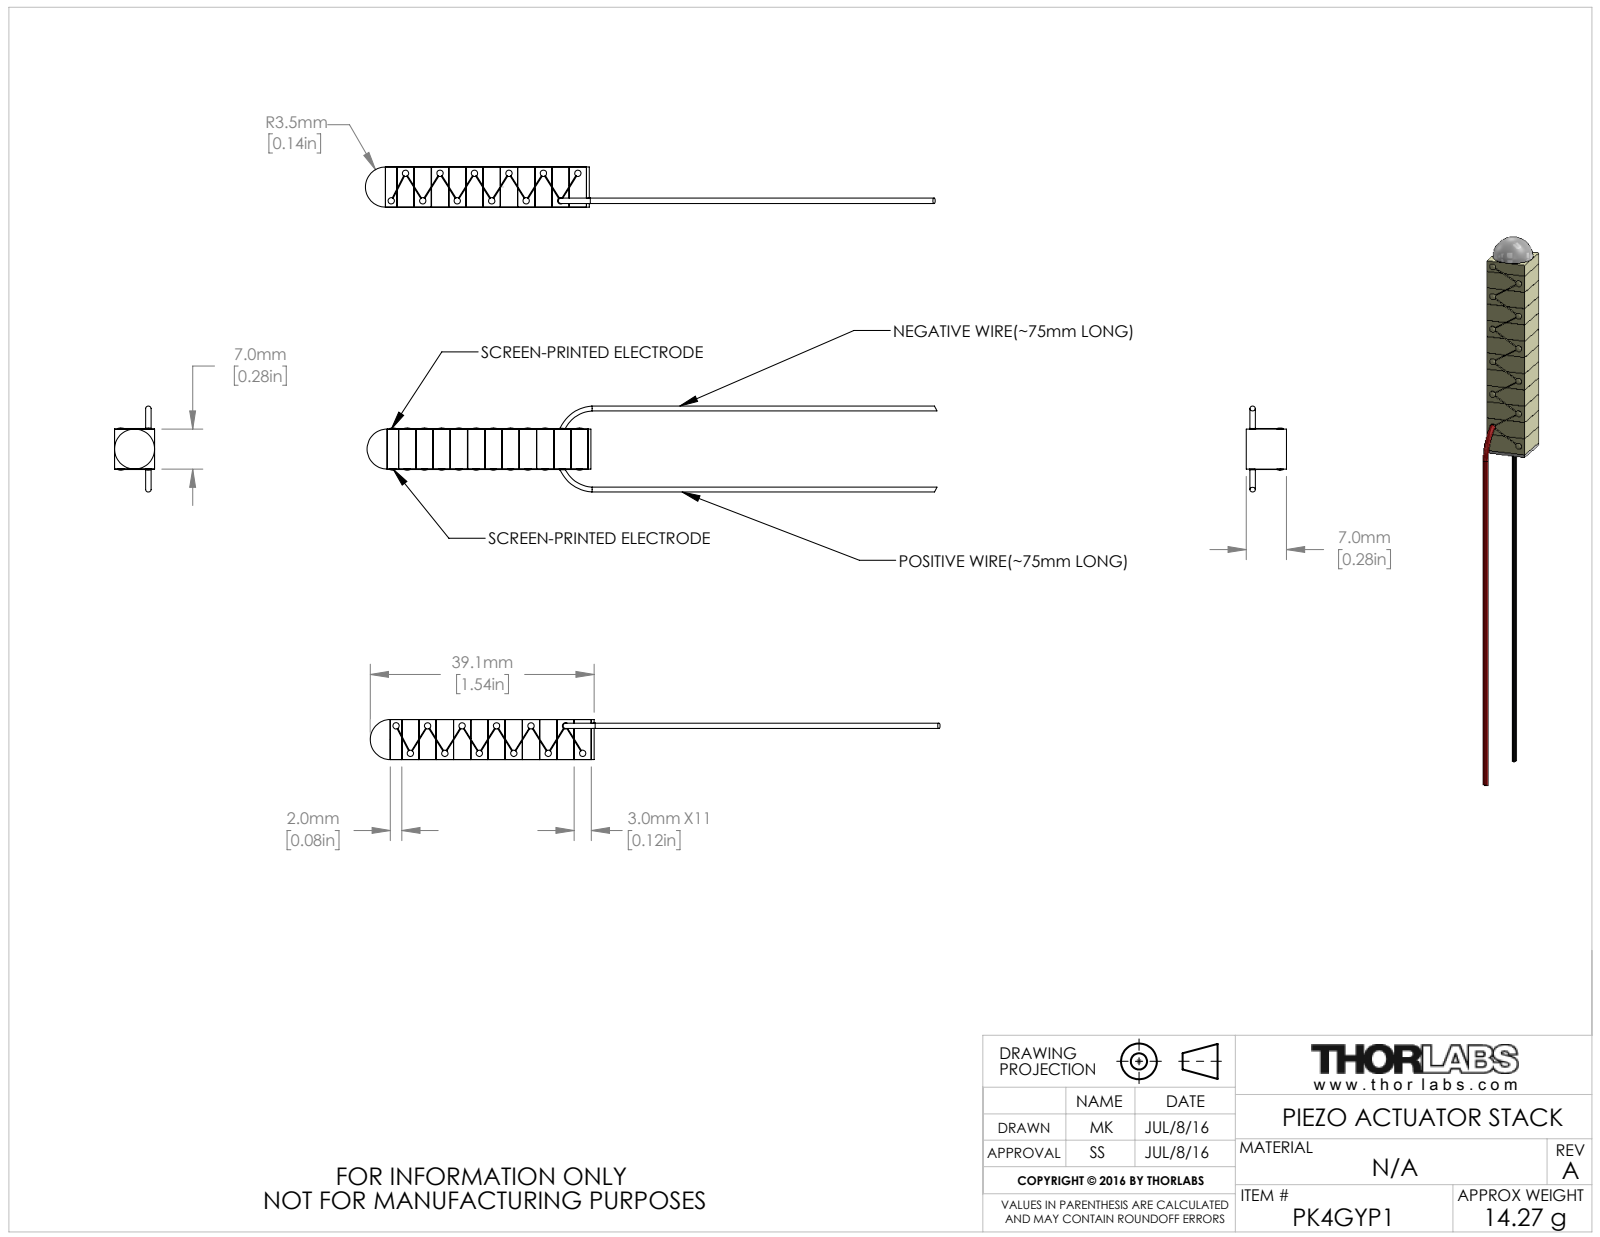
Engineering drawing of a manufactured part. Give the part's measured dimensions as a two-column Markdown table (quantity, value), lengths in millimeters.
| quantity | value |
| --- | --- |
| part name | CTN003161 |
| STEP written by | SolidWorks 2016 (AUTOMOTIVE_DESIGN) |
| units | millimeters |
| bodies | 4 solids, 395 faces (221 planar, 72 cylindrical, 102 other) |
| overall size | 99.5 × 15 × 7 |
| volume | 3 631 mm³ |
| surface area | 4 967 mm² |
| round bosses / shafts (diameter × count) | 1.1 × 12 |
| main face-to-face distances | 3.01, 6.02, 9.03, 7, 3, 12.04, 6.01, 15.05, 12.03, 18.06 |
